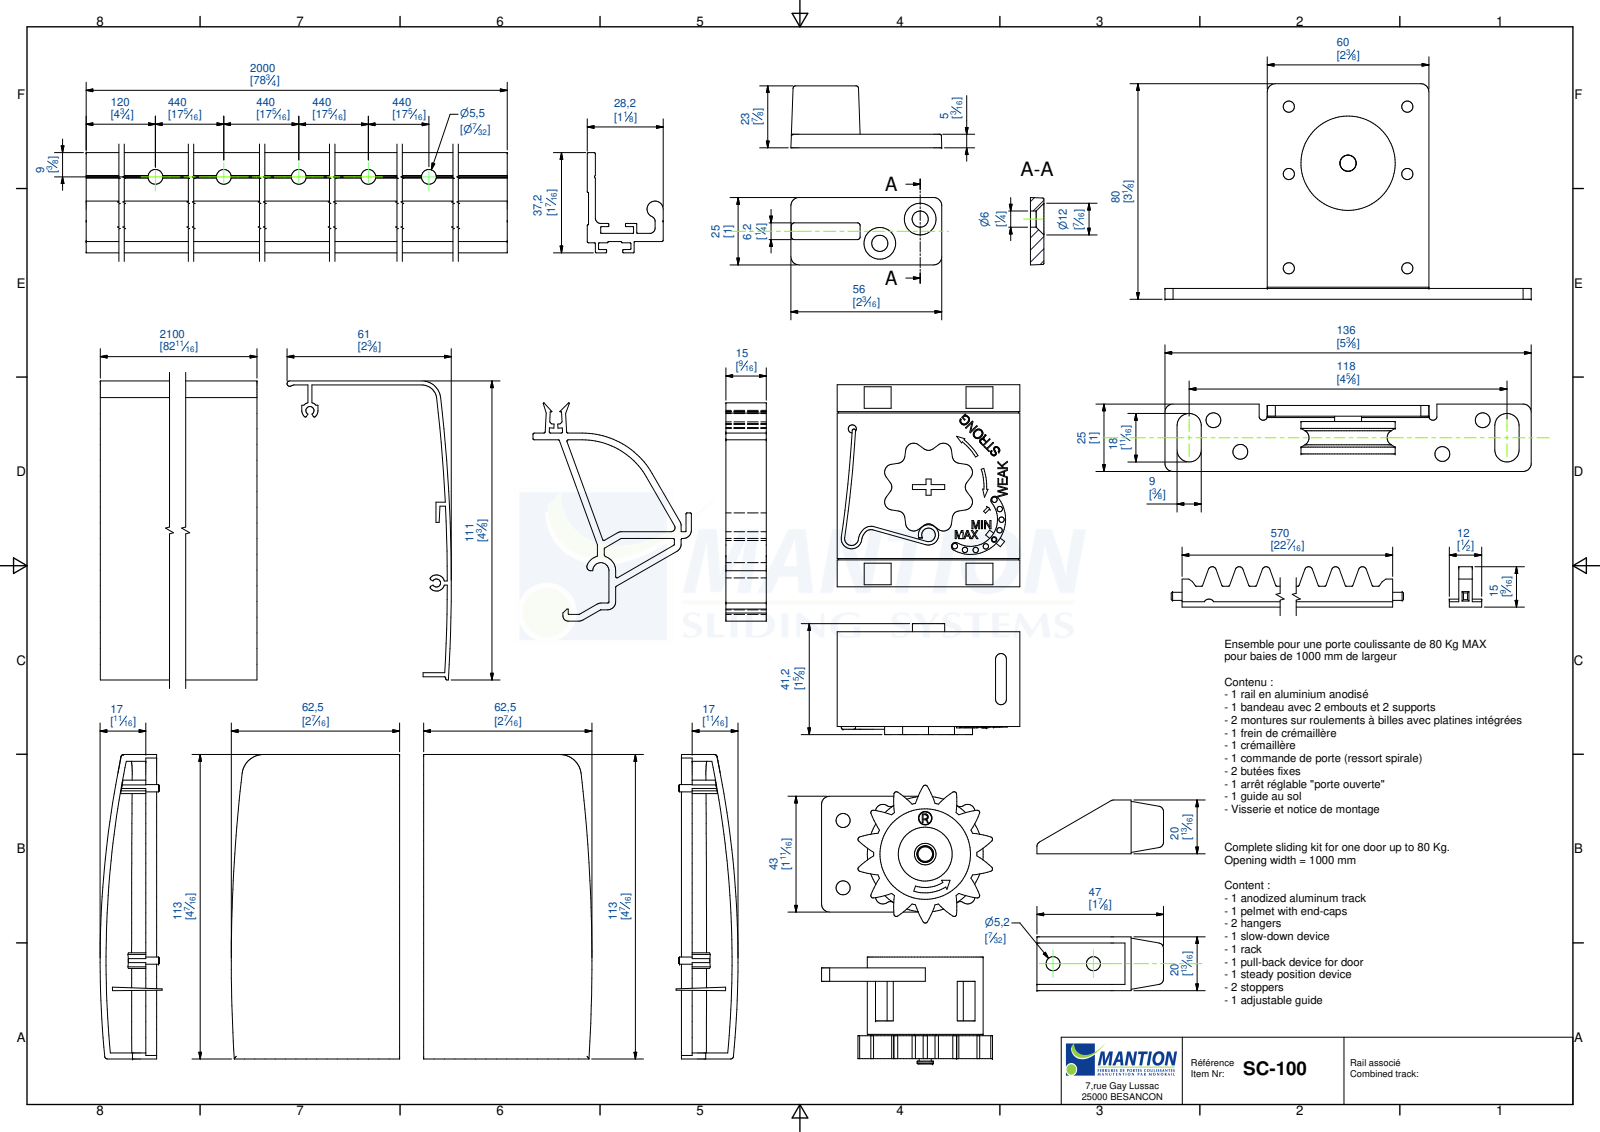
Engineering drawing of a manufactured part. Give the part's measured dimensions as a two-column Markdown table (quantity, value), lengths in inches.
| quantity | value |
| --- | --- |
| part name | Ferme porte meca-45mm-version cale bois MDF; 21595; 21583; 21577 (+8 more) |
| STEP written by | Autodesk Inventor 2019 (AUTOMOTIVE_DESIGN) |
| units | inches |
| bodies | 75 solids, 3503 faces (2078 planar, 1006 cylindrical, 419 other) |
| overall size | 85.33 × 84.016 × 3.327 |
| volume | 99.35 in³ |
| surface area | 2 337 in² |
| round holes (diameter × count) | 0.079 × 20, 0.163 × 14, 0.217 × 13, 0.205 × 6, 0.236 × 6, 0.209 × 5, 0.169 × 4, 0.118 × 3, 0.097 × 2, 0.126 × 2, 0.128 × 2, 0.165 × 2 |
| round bosses / shafts (diameter × count) | 0.177 × 13, 0.344 × 12, 0.197 × 8, 0.394 × 7, 0.157 × 5, 0.354 × 4, 0.189 × 4, 1.378 × 2 |
| partial cylindrical surfaces (radius × count) | 0.02 × 175, 0.059 × 64, 0.118 × 61, 0.079 × 53, 0.012 × 32, 1.299 × 28, 0.039 × 21, 0.035 × 14 |
| main face-to-face distances | 0.059, 0.118, 0.02, 0.098, 2.972, 3.031, 0.146, 4.264, 1.11, 0.992 |
| hole center spacings | 20.866, 1.732, 0.88, 0.984, 1.197, 1.378, 1.763, 1.991 |
